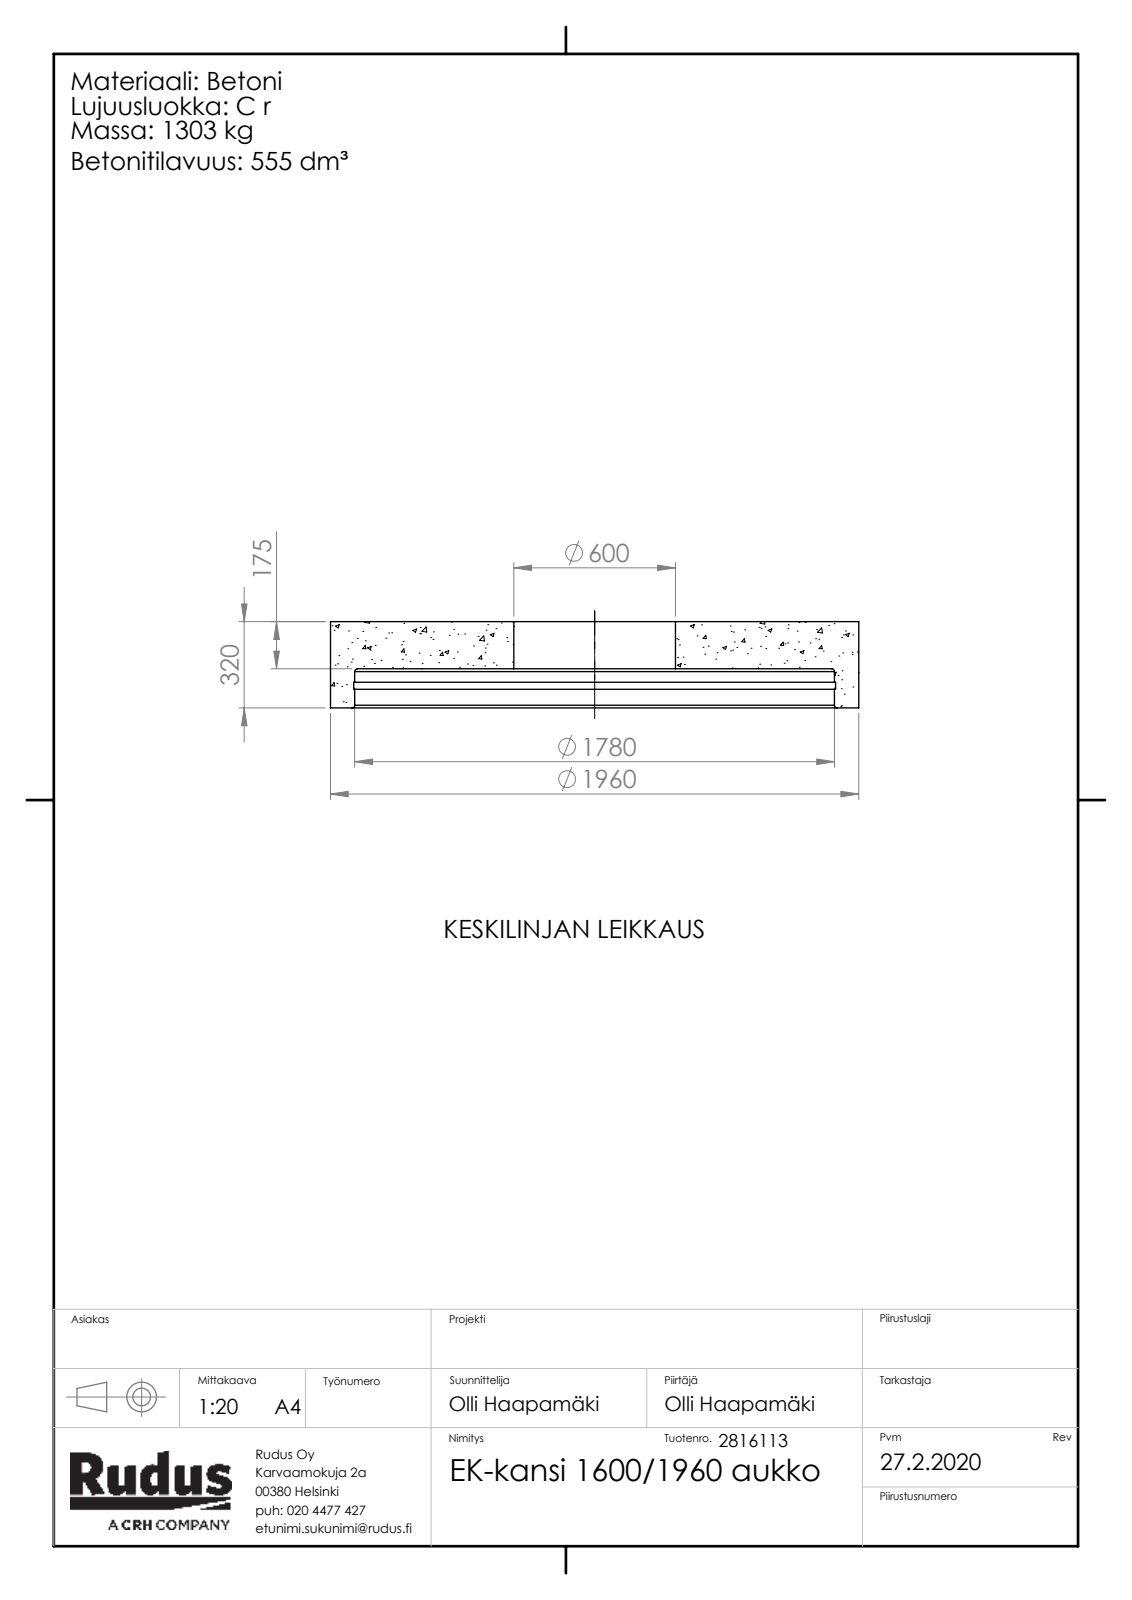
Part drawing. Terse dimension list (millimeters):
name: EK-osa-kansi_Aukko; Rudus 2816113 EK-kansi 1600_1960 aukko
written by: SolidWorks 2019 (CONFIG_CONTROL_DESIGN)
unit: mm
bodies: 1 solid, 96 faces (13 planar, 17 cylindrical, 66 other)
size: 1960 × 1960 × 320
volume: 554 500 000 mm³; area: 8 582 000 mm²
holes: 1× ⌀600, 1× ⌀1780, 1× ⌀1788
bosses: 1× ⌀1960
rounds: 1× R977
face distances: 175, 145, 320, 69, 76, 251, 95, 26, 50, 225
